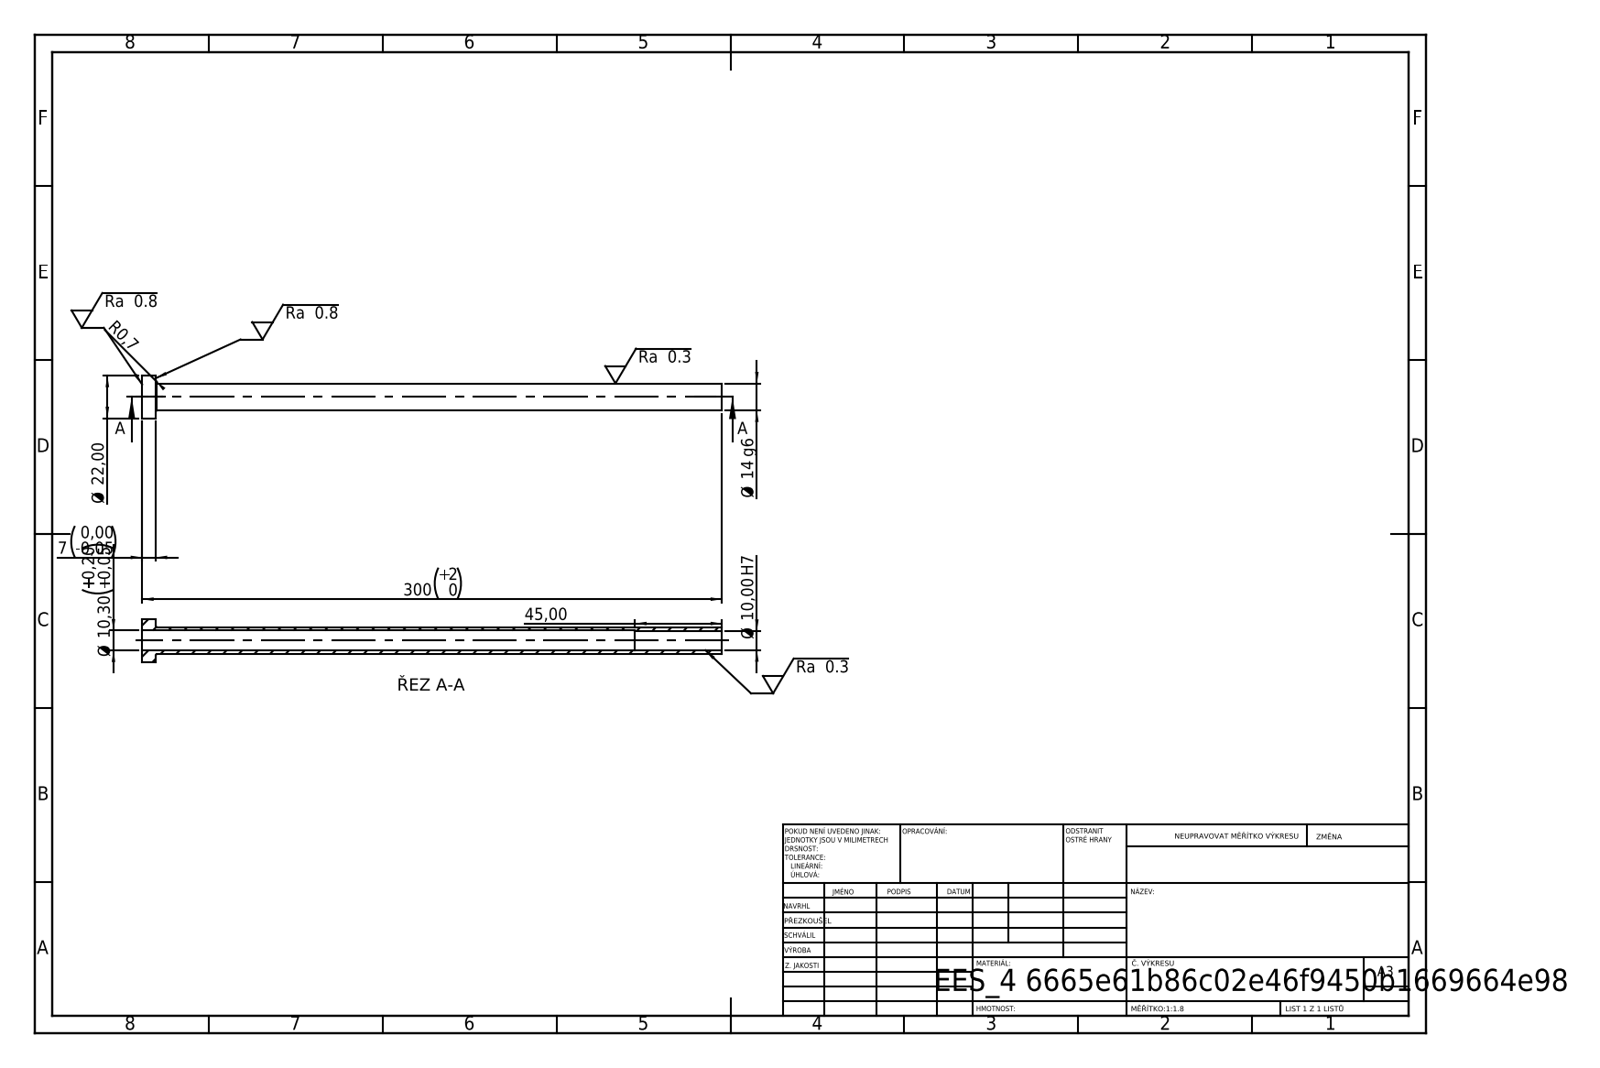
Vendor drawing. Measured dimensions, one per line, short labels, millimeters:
written by: SolidWorks 2019 (CONFIG_CONTROL_DESIGN)
unit: mm
bodies: 1 solid, 14 faces (4 planar, 8 cylindrical, 2 other)
size: 300 × 22 × 22
volume: 22 988 mm³; area: 23 626 mm²
holes: 1× ⌀10, 1× ⌀10.3
bosses: 1× ⌀22, 1× ⌀14
face distances: 7, 300, 293, 255, 248, 45
